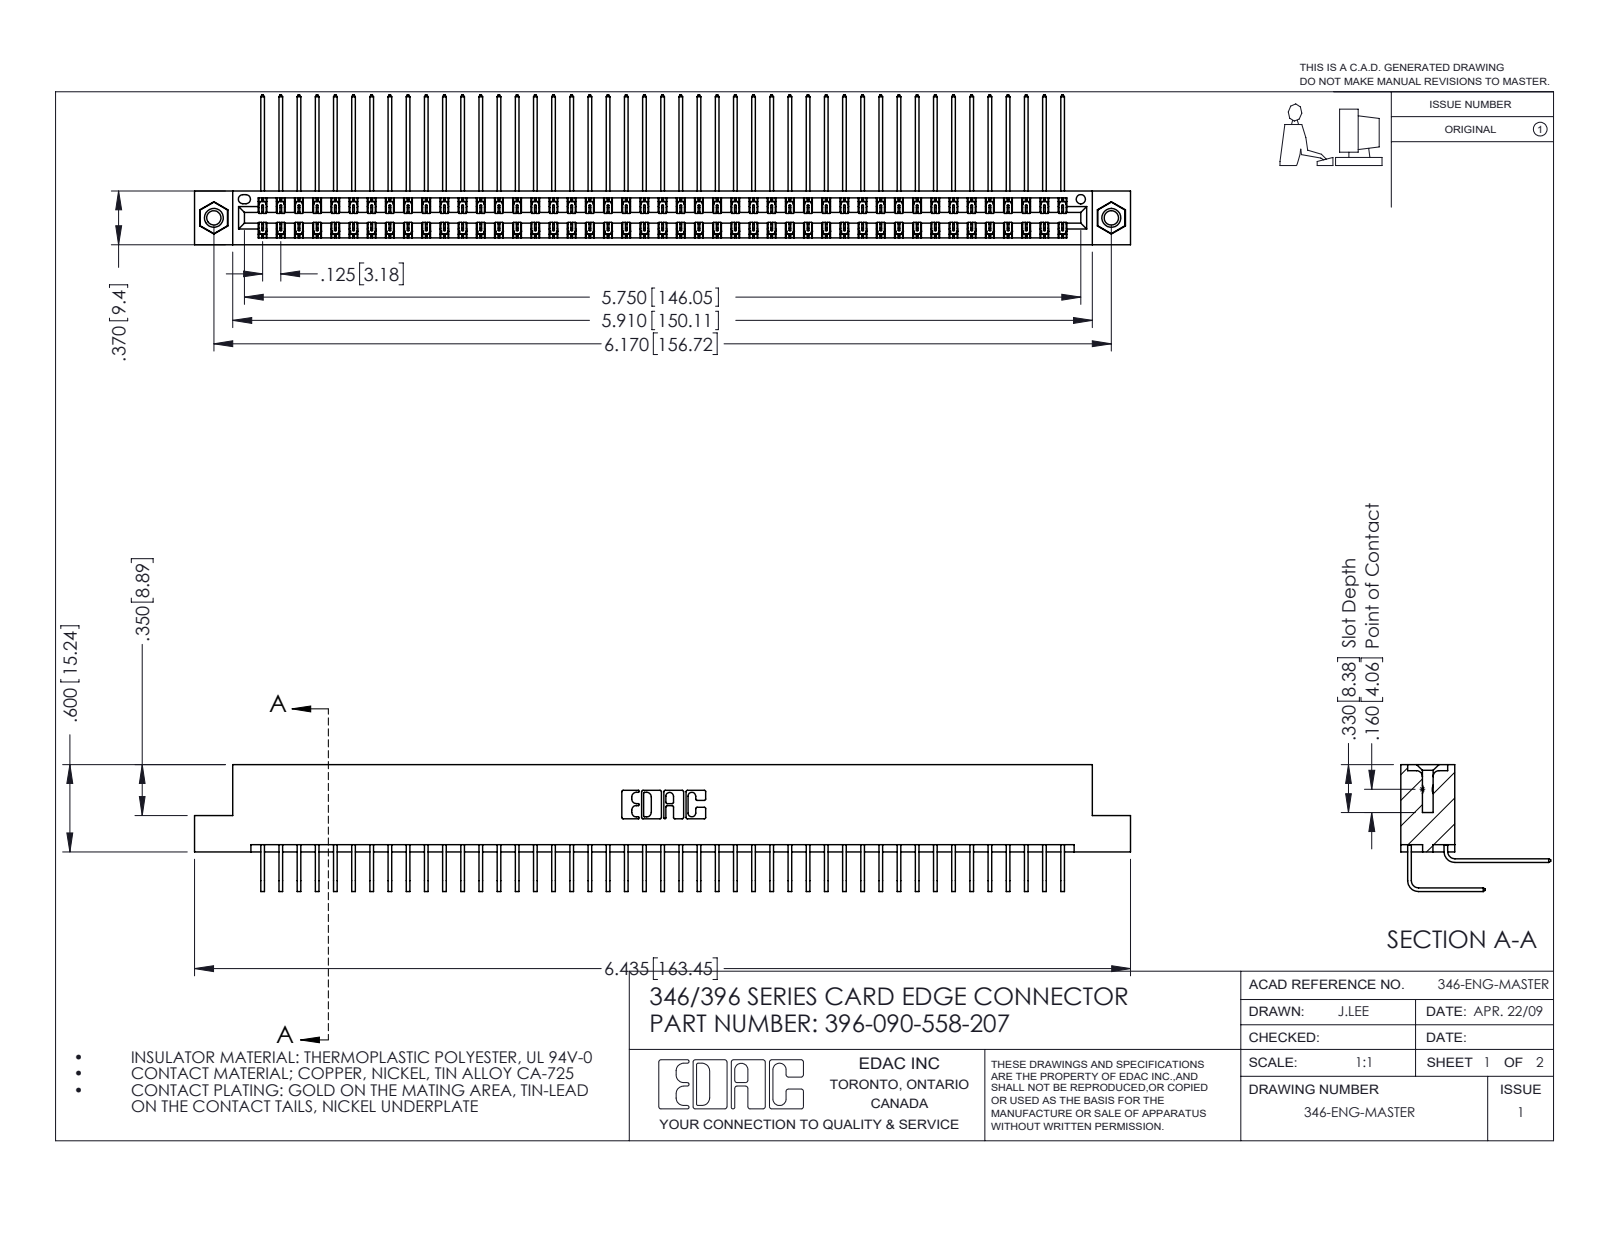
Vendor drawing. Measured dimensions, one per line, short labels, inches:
name: 345-250-001_345-250-005-103; 345-292-001_558 559 Tail - 1; 346 Part_Flush Mounting Lugs - 0.156 Dia-TI; 396-090-558-207 (+1 more)
written by: SolidWorks 2016 (CONFIG_CONTROL_DESIGN)
unit: in
bodies: 93 solids, 5042 faces (3438 planar, 1588 cylindrical, 16 other)
size: 6.435 × 1.03 × 0.873
volume: 1.005 in³; area: 39.07 in²
holes: 2× ⌀0.098, 2× ⌀0.125, 2× ⌀0.156, 1× ⌀0.064
bosses: 2× ⌀0.155
rounds: 135× R0.006, 22× R0.01, 6× R0.007, 6× R0.031, 3× R0.026, 2× R0.014, 2× R0.022, 2× R0.024
face distances: 0.048, 0.322, 0.025, 0.37, 0.072, 0.25, 0.298, 0.275, 0.148, 0.222
hole spacings: 0.246, 5.961, 6.17
